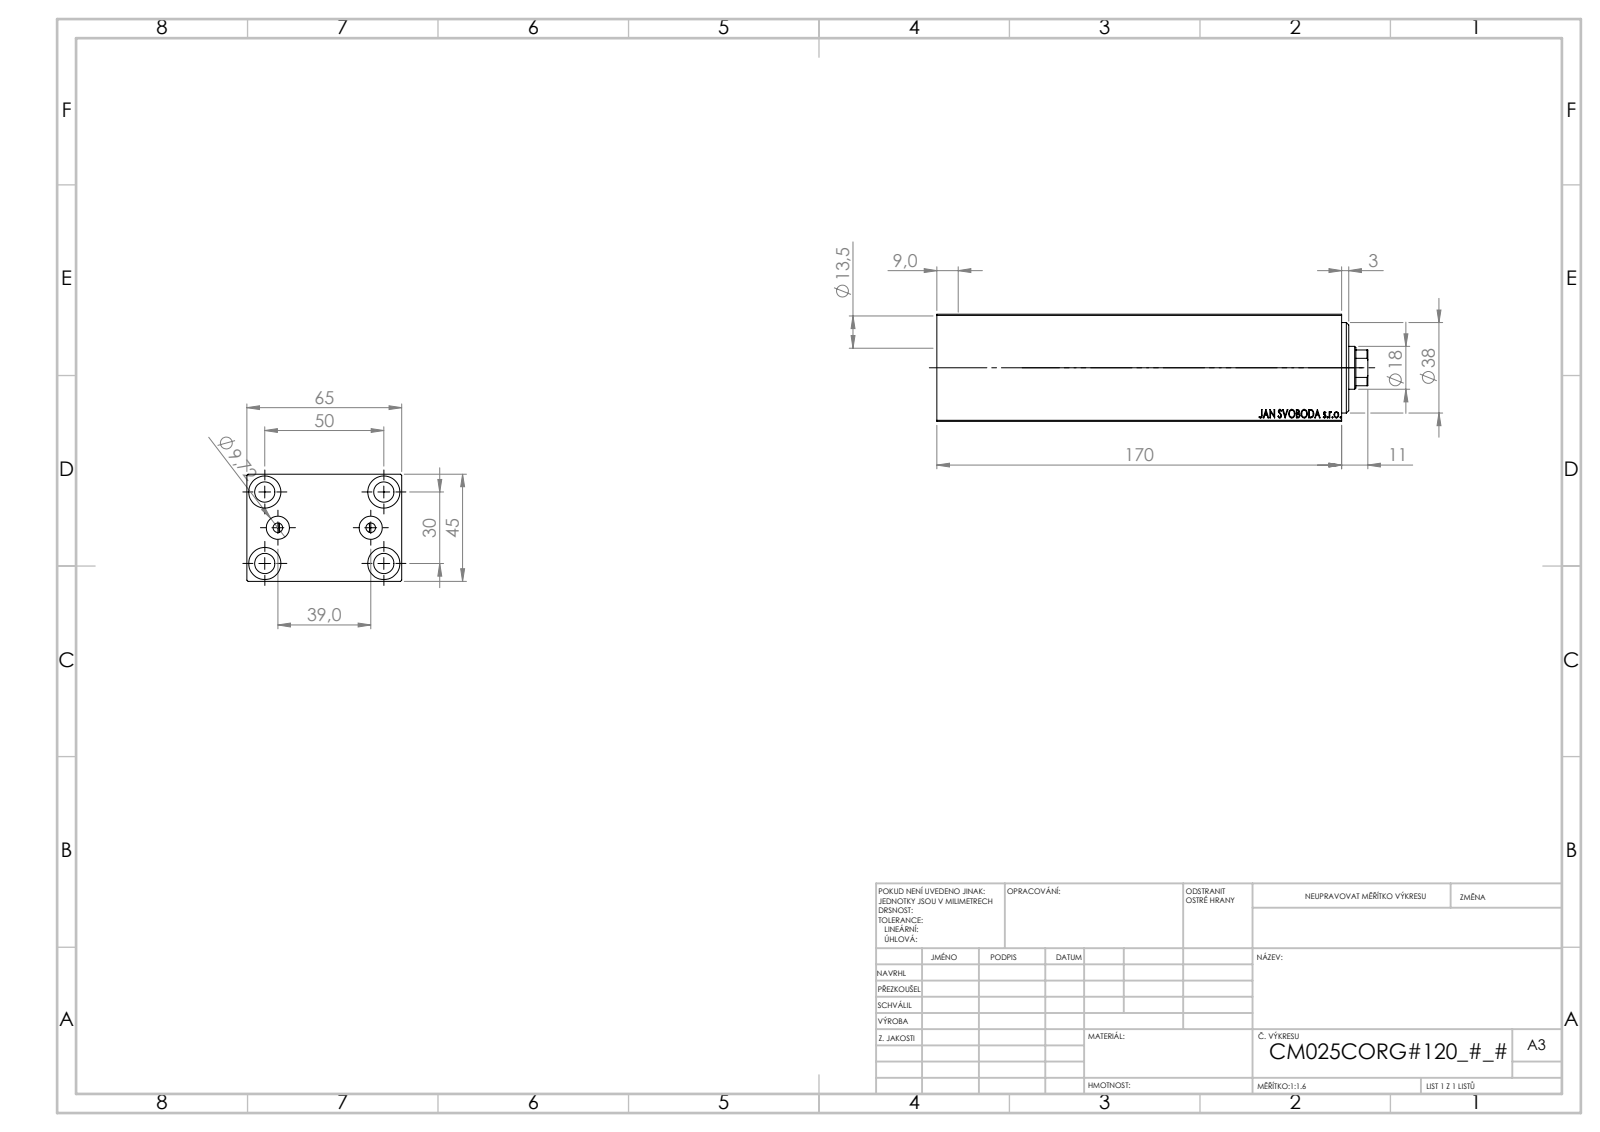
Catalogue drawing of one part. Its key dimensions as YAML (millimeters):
part_name: "V450CM_C_VCP; V450CM_C_Body; V450CM_VC_B"
step_written_by: "SolidWorks 2019 (CONFIG_CONTROL_DESIGN)"
units: millimeters
bodies: {solids: 3, faces: 858, planar: 408, cylindrical: 56, other: 394}
overall_size: [181, 65, 45]
volume: 422590
surface_area: 95506
round_holes:
  - {diameter: 8.5, count: 5}
  - {diameter: 13.5, count: 4}
  - {diameter: 4, count: 2}
  - {diameter: 9.72, count: 2}
  - {diameter: 18, count: 1}
  - {diameter: 21.5, count: 1}
  - {diameter: 25, count: 1}
  - {diameter: 27, count: 1}
  - {diameter: 38, count: 1}
partial_cylinders:
  - {radius: 8.5, count: 1}
face_to_face_distances: [45, 65, 6, 159, 164, 165, 5, 170, 3, 8]
hole_center_spacings: [15.98, 29.15, 46.96, 19.5, 30, 50, 58.31, 39]
